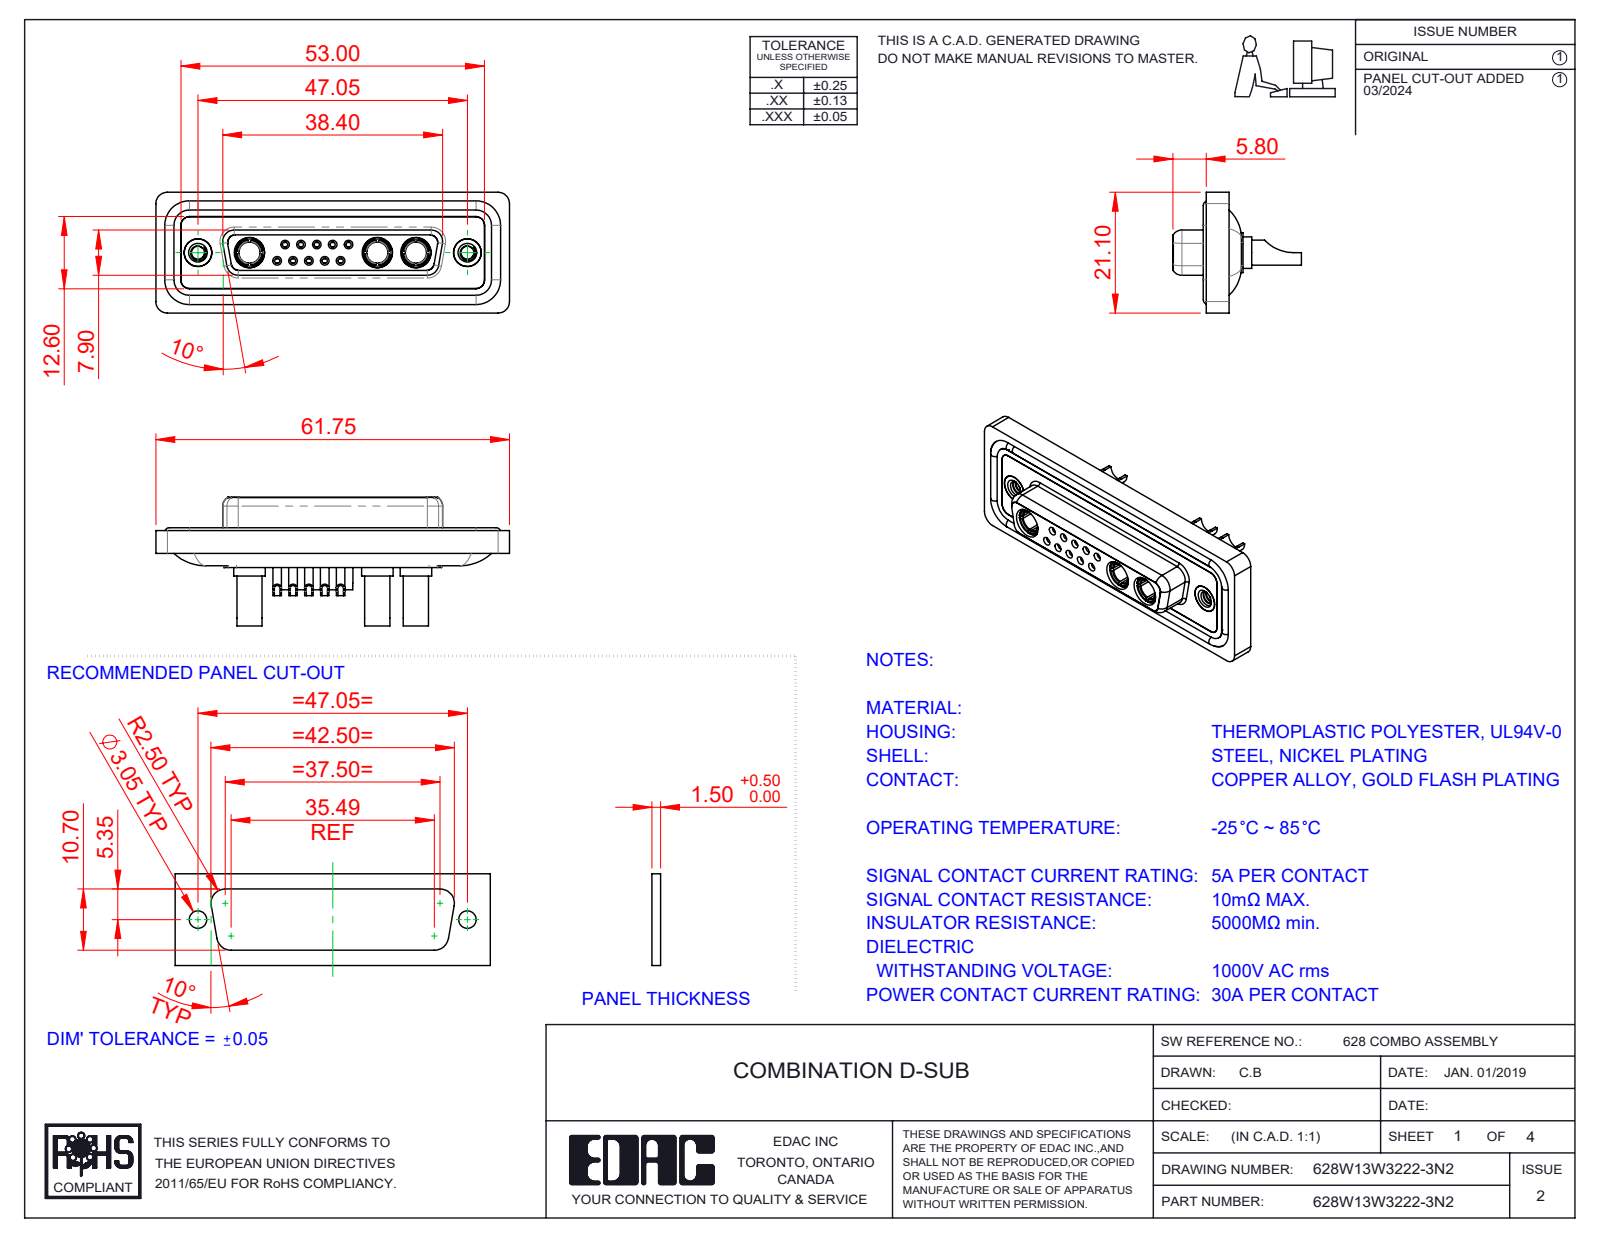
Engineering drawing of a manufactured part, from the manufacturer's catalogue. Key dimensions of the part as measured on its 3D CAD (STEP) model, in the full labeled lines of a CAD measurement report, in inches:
Part name (STEP PRODUCT): Power Socket_30A SC; 628Combo Housing_13W3; 628Combo Shell Rear_25 Contacts; 628Combo Contact Row 2_22 (+5 more)
STEP written by: SolidWorks 2023 (CONFIG_CONTROL_DESIGN)
Units: inches
Bodies: 23 solids, 1176 faces (371 planar, 476 cylindrical, 329 other)
Overall size (bounding box): 2.431 × 0.884 × 0.831
Volume: 0.511 in³ · Surface area: 21.91 in²
Round holes (diameter × count): ⌀0.035 ×10, ⌀0.039 ×10, ⌀0.043 ×10, ⌀0.059 ×10, ⌀0.079 ×10, ⌀0.063 ×5, ⌀0.067 ×5, ⌀0.191 ×5, ⌀0.138 ×3, ⌀0.146 ×3, ⌀0.209 ×3, ⌀0.089 ×2
Round bosses / shafts (diameter × count): ⌀0.087 ×10, ⌀0.063 ×9, ⌀0.217 ×3, ⌀0.205 ×3, ⌀0.195 ×3, ⌀0.187 ×3, ⌀0.173 ×3, ⌀0.148 ×3
Partial cylindrical surfaces — rounded edges, fillets, slot ends (radius × count): R0.059 ×22, R0.079 ×18, R0.053 ×8, R0.063 ×8, R0.039 ×6, R0.01 ×4, R0.02 ×4, R0.024 ×4
Main face-to-face distances: 0.016, 0.071, 0.293, 0.222, 0.02, 0.26, 0.278, 0.063, 0.114, 0.043
Hole centre spacings: 0.124, 0.109, 0.198, 0.198, 0.218, 0.327, 0.295, 0.109
